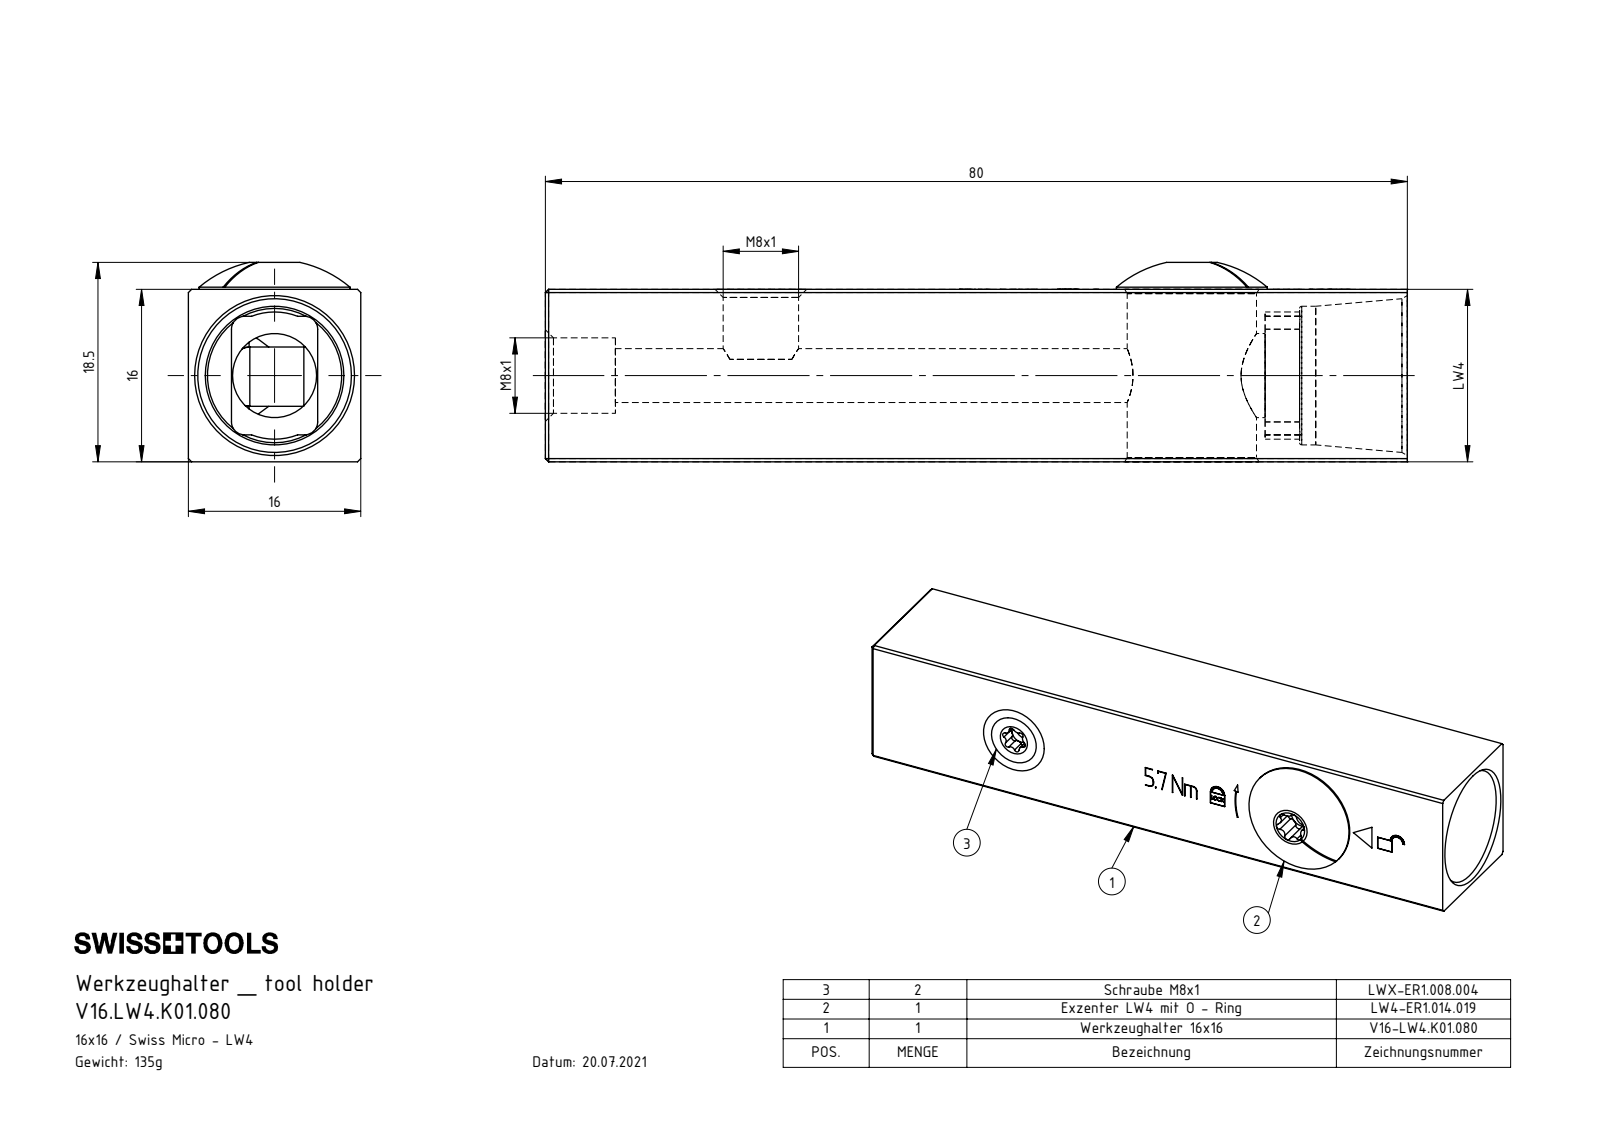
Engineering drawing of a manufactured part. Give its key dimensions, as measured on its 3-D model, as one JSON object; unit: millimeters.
{"part_name": "LW4-ER1.014.019; V16.LW4.K01.080; DIN 3771 - 10x1; V16-LW4.K01.080_D (+2 more)", "step_written_by": "SolidWorks 2022 (AUTOMOTIVE_DESIGN)", "units": "millimeters", "bodies": {"solids": 6, "faces": 206, "planar": 95, "cylindrical": 70, "other": 41}, "overall_size": [80, 18.5, 16], "volume_mm3": 17213, "surface_area_mm2": 9153, "round_holes": [[2.4, 2], [7, 2], [1, 1], [2.85, 1], [5, 1], [7.8, 1], [12.86, 1]], "round_bosses_or_shafts": [[8, 2], [14, 1], [12, 1], [10.2, 1]], "partial_cylinders_radius": [[0.34, 12], [0.59, 12], [0.4, 6], [0.69, 6], [1.2, 4], [2.75, 2], [4.1, 1], [4.15, 1]], "face_to_face_distances": [16, 4, 15.7, 12, 2.5, 80, 13.2, 1.4, 22.2, 1.1], "hole_center_spacings": [40]}
